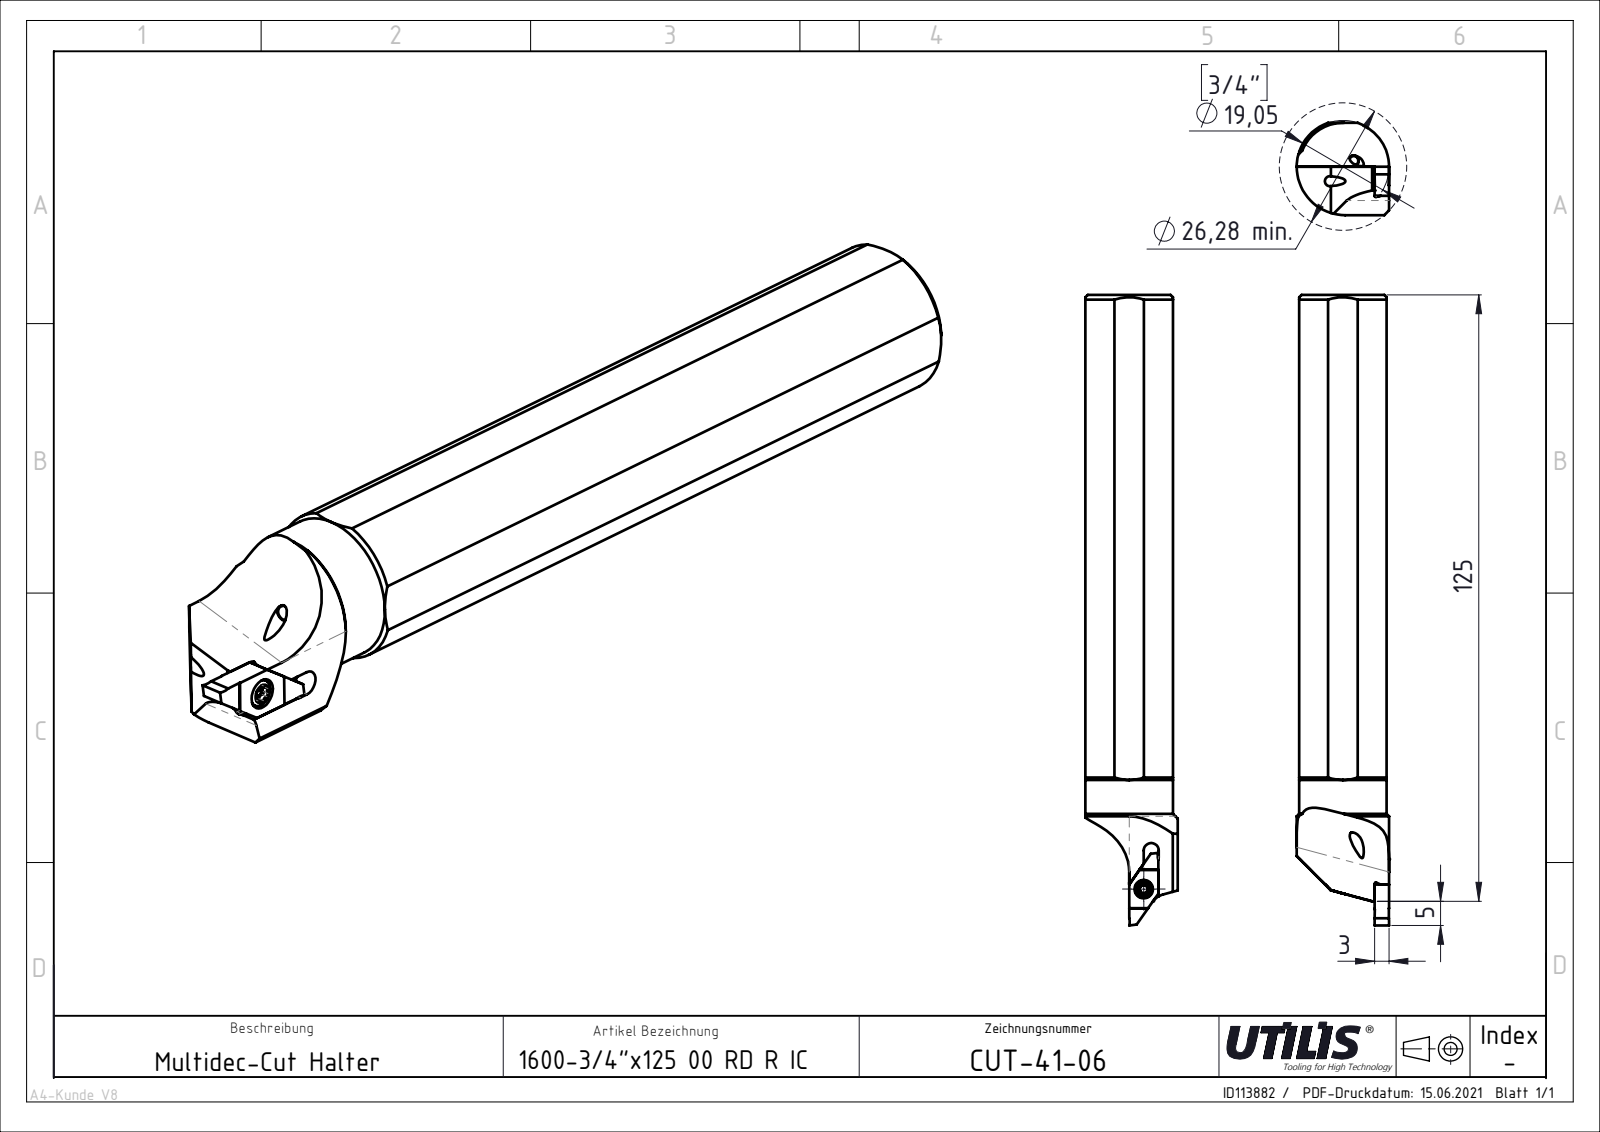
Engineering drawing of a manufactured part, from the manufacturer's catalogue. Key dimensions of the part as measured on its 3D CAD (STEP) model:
Part name (STEP PRODUCT): CUT-41-06; CUT-41-Vorlage 1600-Kunde_Dfaut; CUT-41-Kunde_06; MSP-7_M2,5X6-TX8 CERATIZIT Schraube
STEP written by: SolidWorks 2013 (CONFIG_CONTROL_DESIGN)
Units: millimetres
Bodies: 3 solids, 114 faces (31 planar, 46 cylindrical, 37 other)
Overall size (bounding box): 130 × 19.28 × 19.05
Volume: 29 005 mm³ · Surface area: 10 149 mm²
Round holes (diameter × count): ⌀2 ×1, ⌀2.05 ×1, ⌀2.2 ×1, ⌀3 ×1, ⌀6 ×1, ⌀8.8 ×1
Round bosses / shafts (diameter × count): ⌀18.05 ×1, ⌀3.45 ×1, ⌀2.5 ×1
Partial cylindrical surfaces — rounded edges, fillets, slot ends (radius × count): R0.2 ×6, R0.45 ×6, R0.4 ×2, R2.9 ×2, R4 ×1, R9.53 ×1, R10 ×1
Main face-to-face distances: 18.04, 18.05, 9.02, 18.55, 0.5, 0.98, 10, 19.02, 3, 15.55
